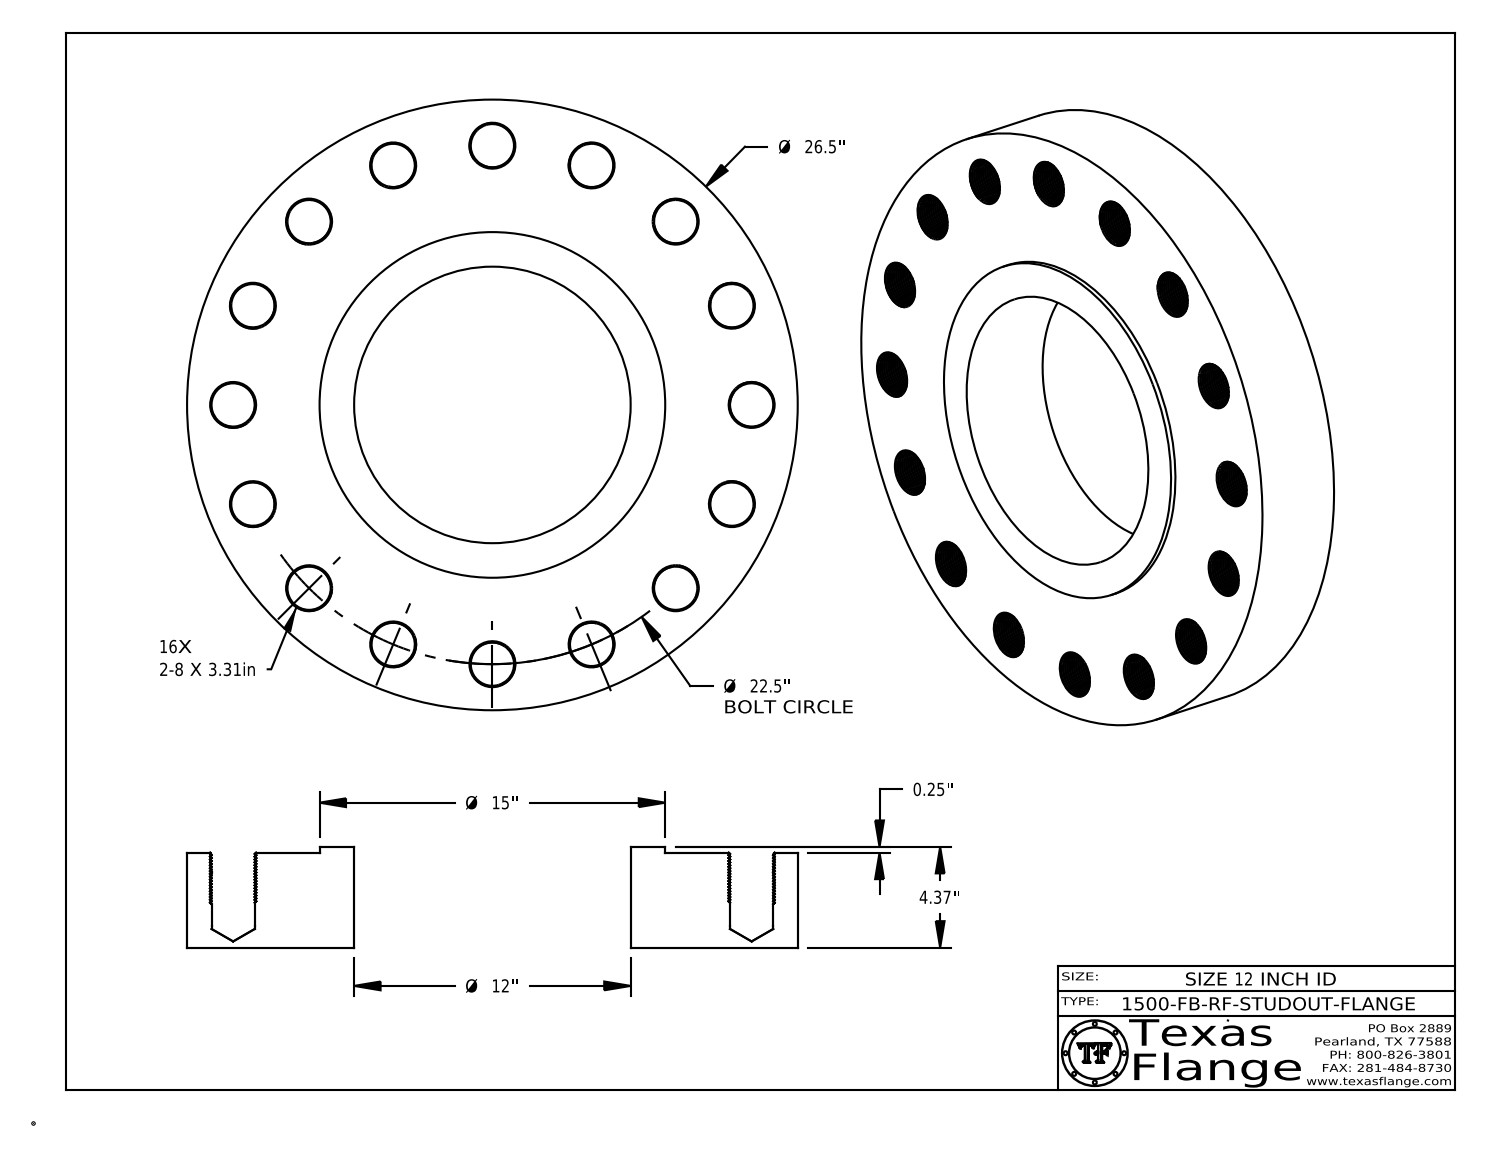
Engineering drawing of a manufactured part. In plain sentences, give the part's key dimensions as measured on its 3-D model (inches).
The part is named "12-1500-FB-RF-STUDOUT-FLANGE". Its 3-D file was written by "CATIA V5 STEP AP214 (AUTOMOTIVE_DESIGN)". It is 1 solid with 2250 faces: 368 planar, 634 cylindrical and 1248 other. Overall it measures 26.5 by 26.5 by 4.37 inches. Its volume is 1 662 cubic inches and its surface area 1 806 square inches. Round holes: 16 of diameter 1.875, 1 of diameter 1, 1 of diameter 12. Round bosses or shafts: 8 of diameter 0.061, 1 of diameter 26.5, 1 of diameter 15, 1 of diameter 0.788. The main face-to-face distances are 4.12, 0.25, 4.37, 4.355, 4.105, 0.015, 0.298, 0.293, 0.054, 0.248. The hole center spacings are 12.5, 20.787, 22.068, 8.611, 11.25, 15.91, 4.389, 4.39.
